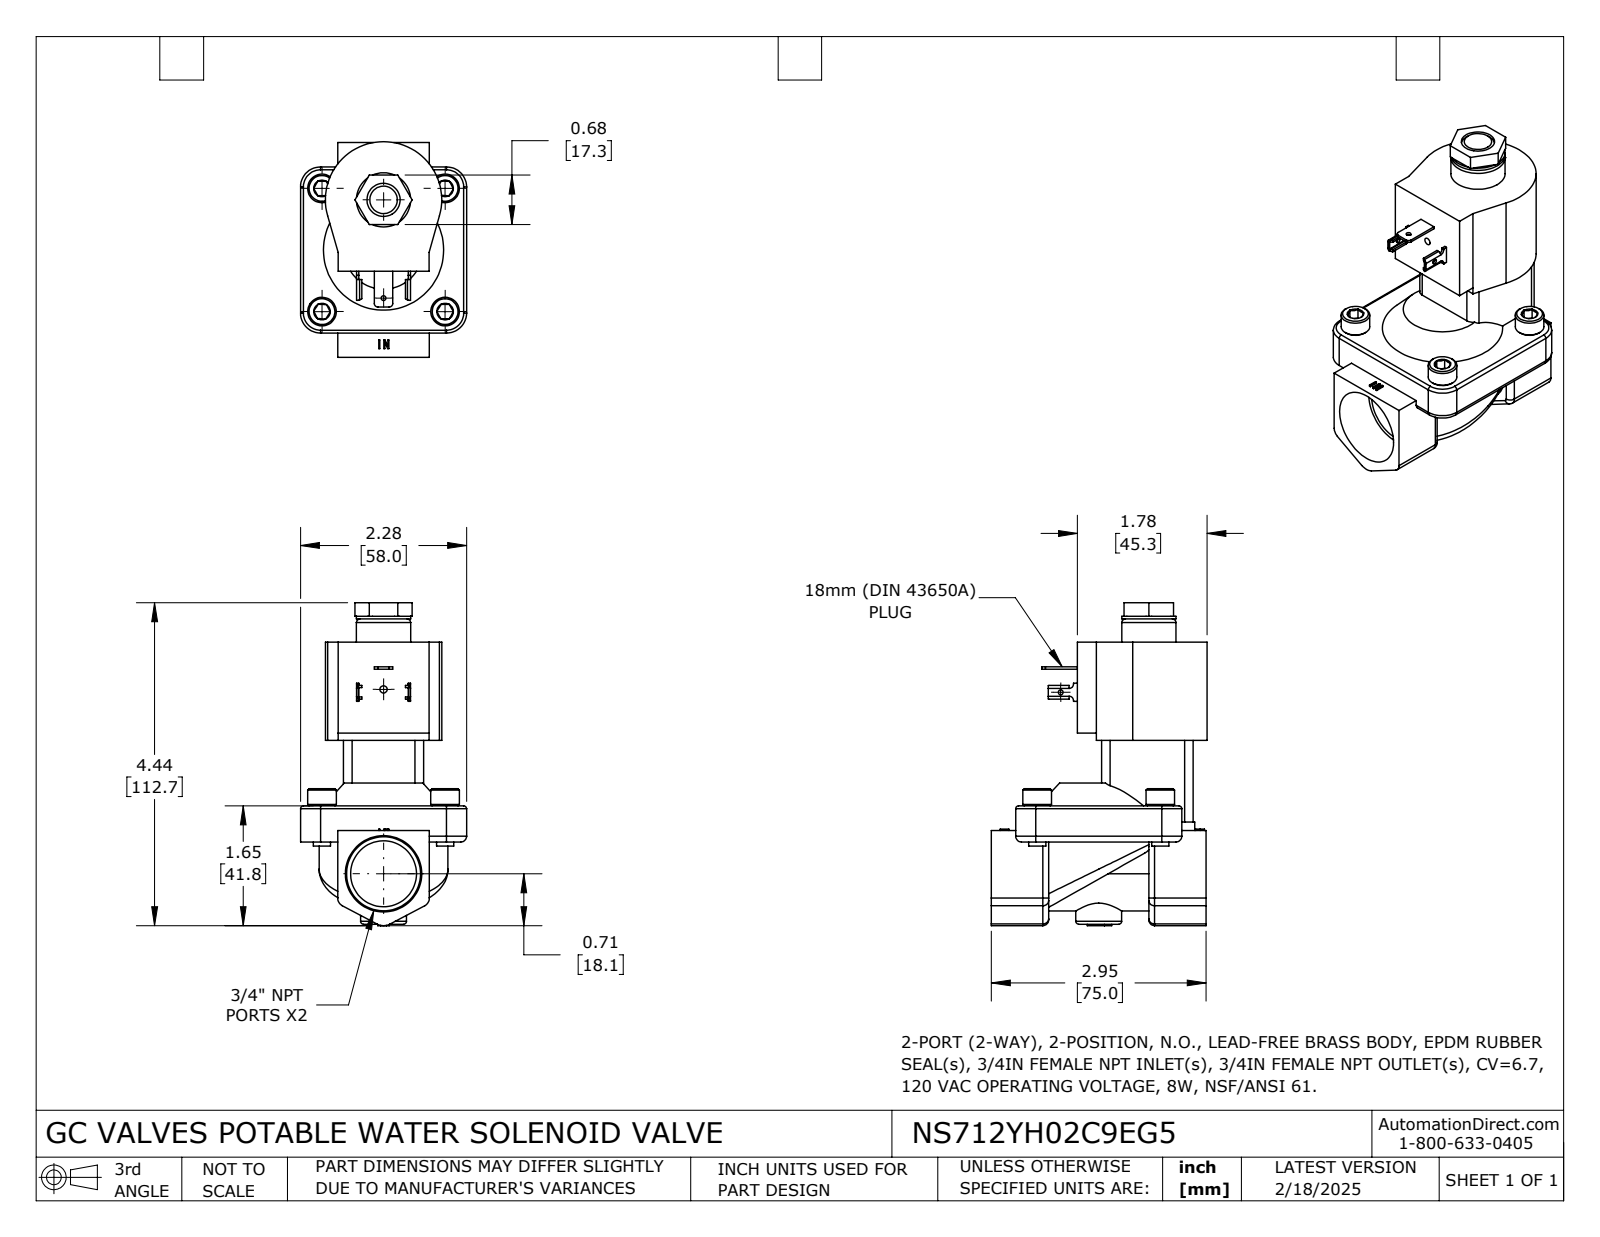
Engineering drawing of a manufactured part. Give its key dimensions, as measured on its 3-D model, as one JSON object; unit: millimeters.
{"part_name": "NS712YH02C9EG5", "step_written_by": "SolidWorks 2024 (CONFIG_CONTROL_DESIGN)", "units": "millimeters", "bodies": {"solids": 1, "faces": 379, "planar": 195, "cylindrical": 95, "other": 89}, "overall_size": [112.71, 75.32, 58], "volume_mm3": 161462, "surface_area_mm2": 32099, "round_holes": [[1.68, 1], [1.7, 1], [2.53, 1], [11.58, 1], [23.01, 1], [30.48, 1]], "round_bosses_or_shafts": [[10, 4], [6, 4], [18.95, 1], [16, 1]], "partial_cylinders_radius": [[2, 11], [3, 6], [0.15, 4], [1, 4], [1.04, 4], [7, 4], [1.27, 2], [1.52, 2]], "face_to_face_distances": [30, 2, 57.19, 32, 43, 15, 13, 45, 12.6, 69.79], "hole_center_spacings": [34.29, 64.36]}
